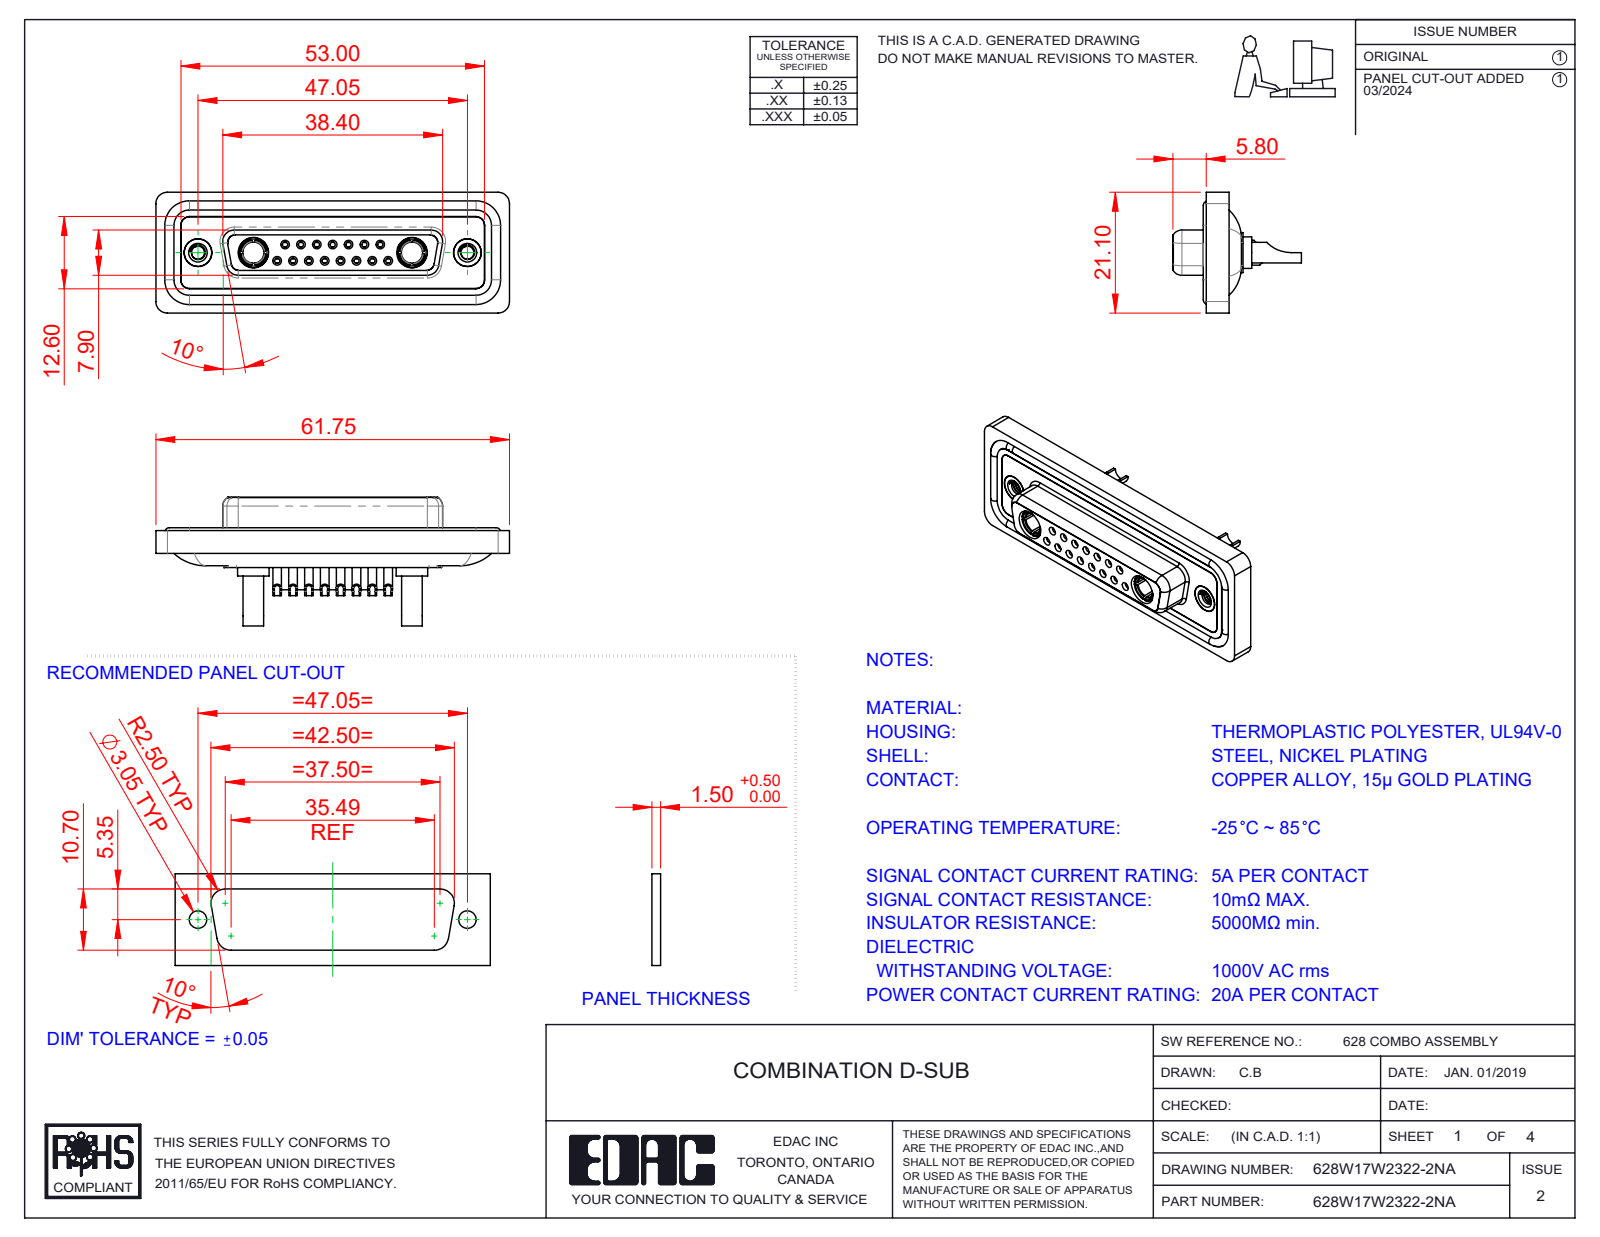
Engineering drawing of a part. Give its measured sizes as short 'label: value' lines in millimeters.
name: 628Combo Waterproof Housing_25 Contacts; 628Combo Contact Row 1_22; 628Combo Contact Row 2_22; 628W17W2322-2NA (+5 more)
written by: SolidWorks 2023 (CONFIG_CONTROL_DESIGN)
unit: mm
bodies: 26 solids, 1369 faces (424 planar, 557 cylindrical, 388 other)
size: 61.75 × 22.45 × 21.1
volume: 8 383 mm³; area: 14 178 mm²
holes: 15× ⌀0.9, 15× ⌀1, 15× ⌀1.1, 15× ⌀1.5, 15× ⌀2, 8× ⌀1.6, 7× ⌀1.7, 4× ⌀4.85, 2× ⌀2.26, 2× ⌀2.7, 2× ⌀3.7, 2× ⌀4
bosses: 15× ⌀2.2, 11× ⌀1.6, 2× ⌀5.5, 2× ⌀5.2, 2× ⌀4.96, 2× ⌀4.95, 2× ⌀4.8, 2× ⌀4.75
rounds: 22× R1.5, 18× R2, 8× R1.35, 8× R1.6, 6× R1, 4× R0.25, 4× R0.5, 4× R0.6
face distances: 0.4, 1.8, 7.45, 5.65, 6.6, 0.5, 7.05, 1.6, 2.9, 1.1
hole spacings: 3.16, 2.77, 8.31, 5.54, 5.03, 5.04, 7.49, 11.08
